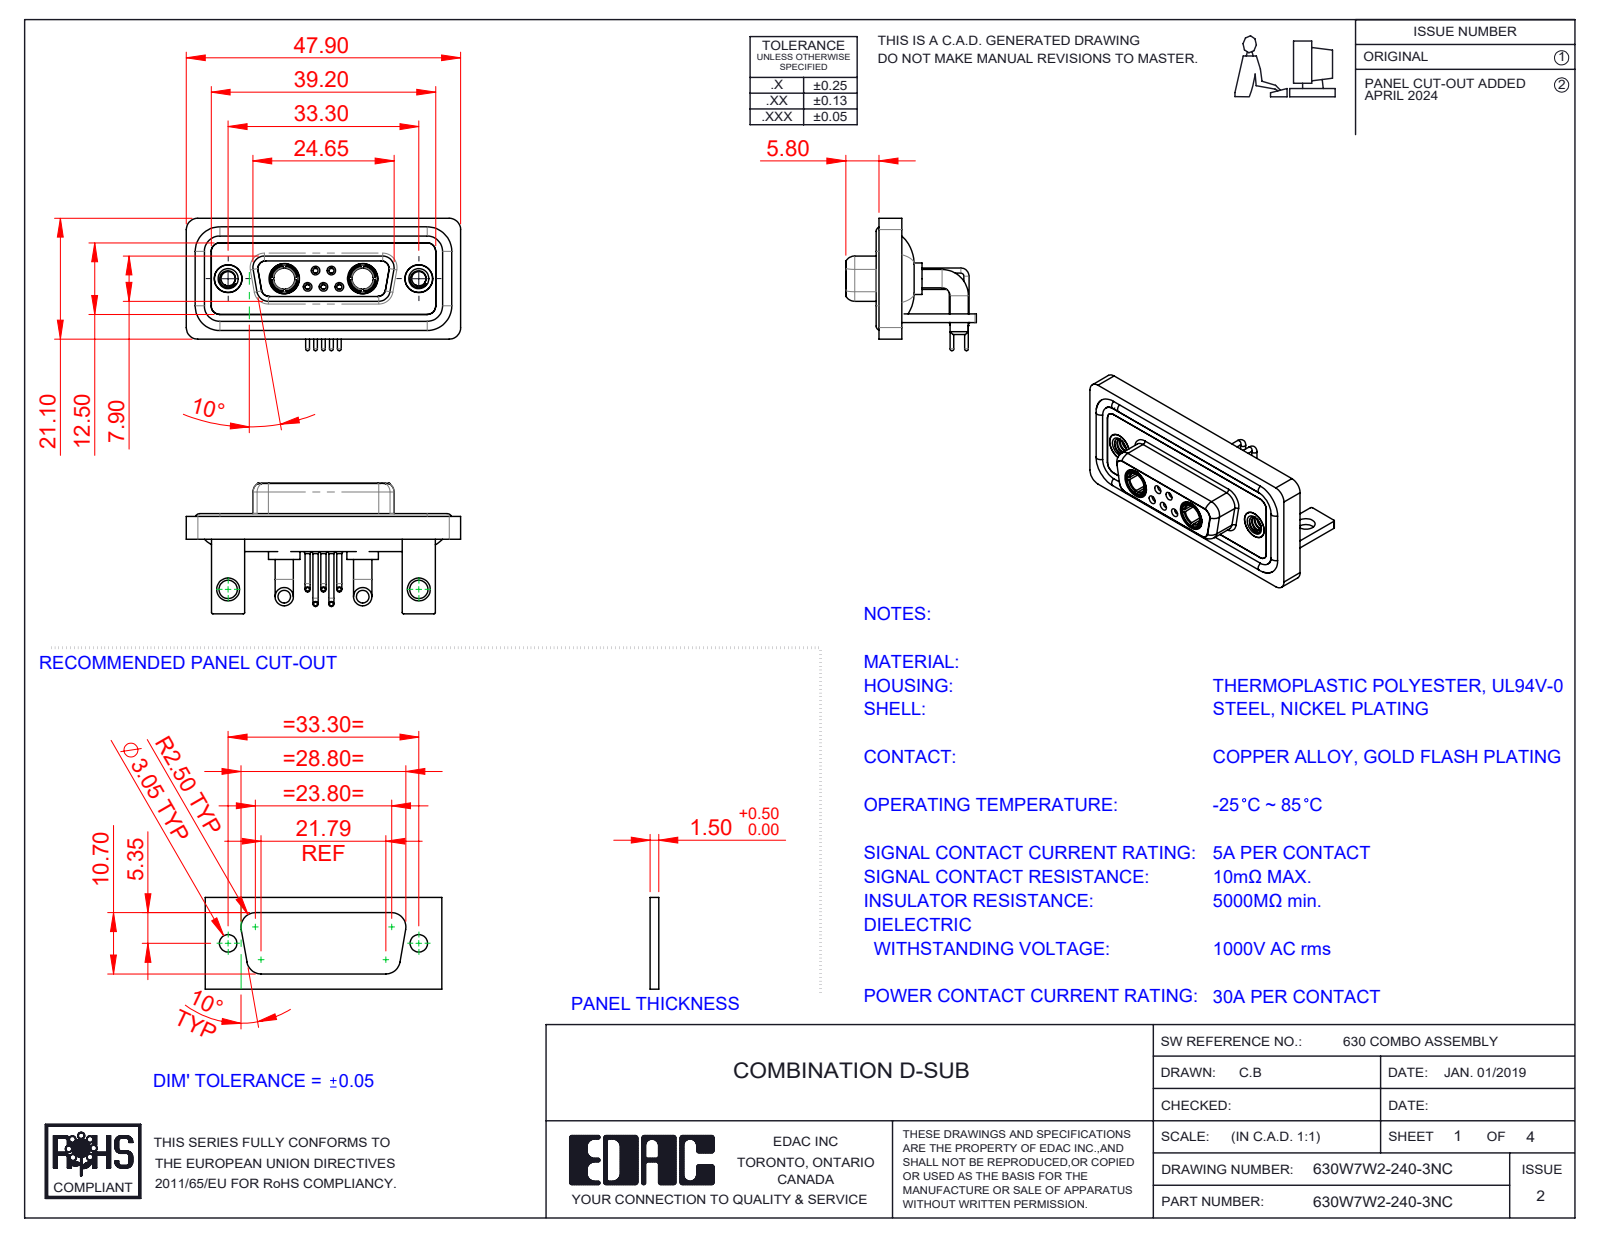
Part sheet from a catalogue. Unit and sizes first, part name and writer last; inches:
Units: inches
Overall size (bounding box): 1.886 × 0.91 × 0.898
Round holes (diameter × count): ⌀0.035 ×5, ⌀0.043 ×5, ⌀0.059 ×5, ⌀0.079 ×5, ⌀0.191 ×4, ⌀0.063 ×3, ⌀0.067 ×2, ⌀0.098 ×2, ⌀0.126 ×2, ⌀0.146 ×2, ⌀0.157 ×2, ⌀0.159 ×2
Round bosses / shafts (diameter × count): ⌀0.063 ×6, ⌀0.035 ×5, ⌀0.026 ×5, ⌀0.126 ×4, ⌀0.217 ×2, ⌀0.205 ×2, ⌀0.195 ×2, ⌀0.195 ×2
Partial cylindrical surfaces — rounded edges, fillets, slot ends (radius × count): R0.079 ×21, R0.059 ×18, R0.01 ×16, R0.053 ×12, R0.063 ×8, R0.02 ×5, R0.024 ×4, R0.026 ×4
Main face-to-face distances: 0.016, 0.114, 0.059, 0.071, 0.146, 0.043, 0.161, 0.063, 0.098, 0.055
Hole centre spacings: 0.124, 0.109, 0.386, 0.925, 1.311, 0.17, 0.17, 0.198
Volume: 0.403 in³ · Surface area: 17.02 in²
Bodies: 18 solids, 849 faces (258 planar, 375 cylindrical, 216 other)
Part name (STEP PRODUCT): 630Combo Housing_7W2; 630Combo Shell Rear_15 Contacts; Power Socket_30A RA; 630Combo Contact Row 1_50 Contacts (+6 more)
STEP written by: SolidWorks 2023 (CONFIG_CONTROL_DESIGN)
